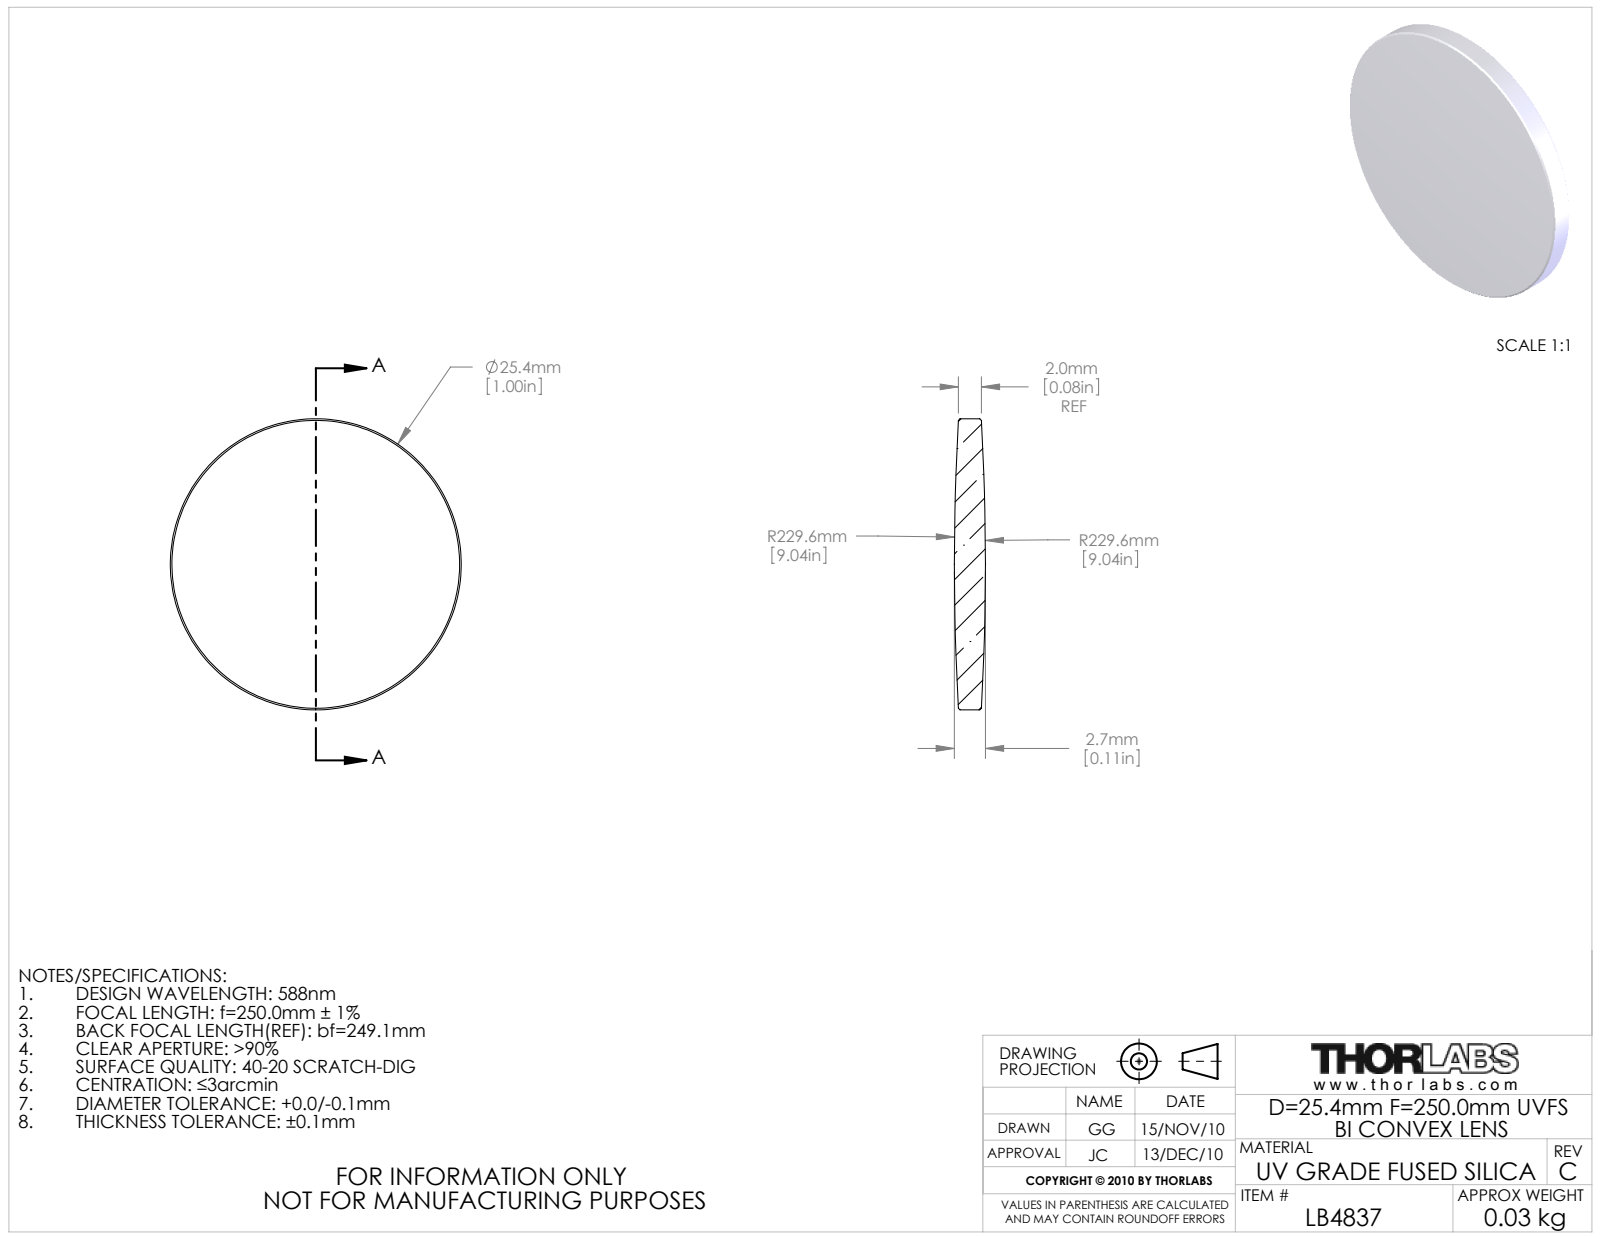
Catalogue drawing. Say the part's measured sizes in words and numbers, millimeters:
The part is named "3408-E0W". Its 3-D file was written by "SolidWorks 2009 (AUTOMOTIVE_DESIGN)". It is 1 solid with 10 faces: 0 planar, 2 cylindrical and 8 other. Overall it measures 25.4 by 25.4 by 2.7 millimeters. Its volume is 1 186 cubic millimeters and its surface area 1 161 square millimeters. Round bosses or shafts: 1 of diameter 25.4.
